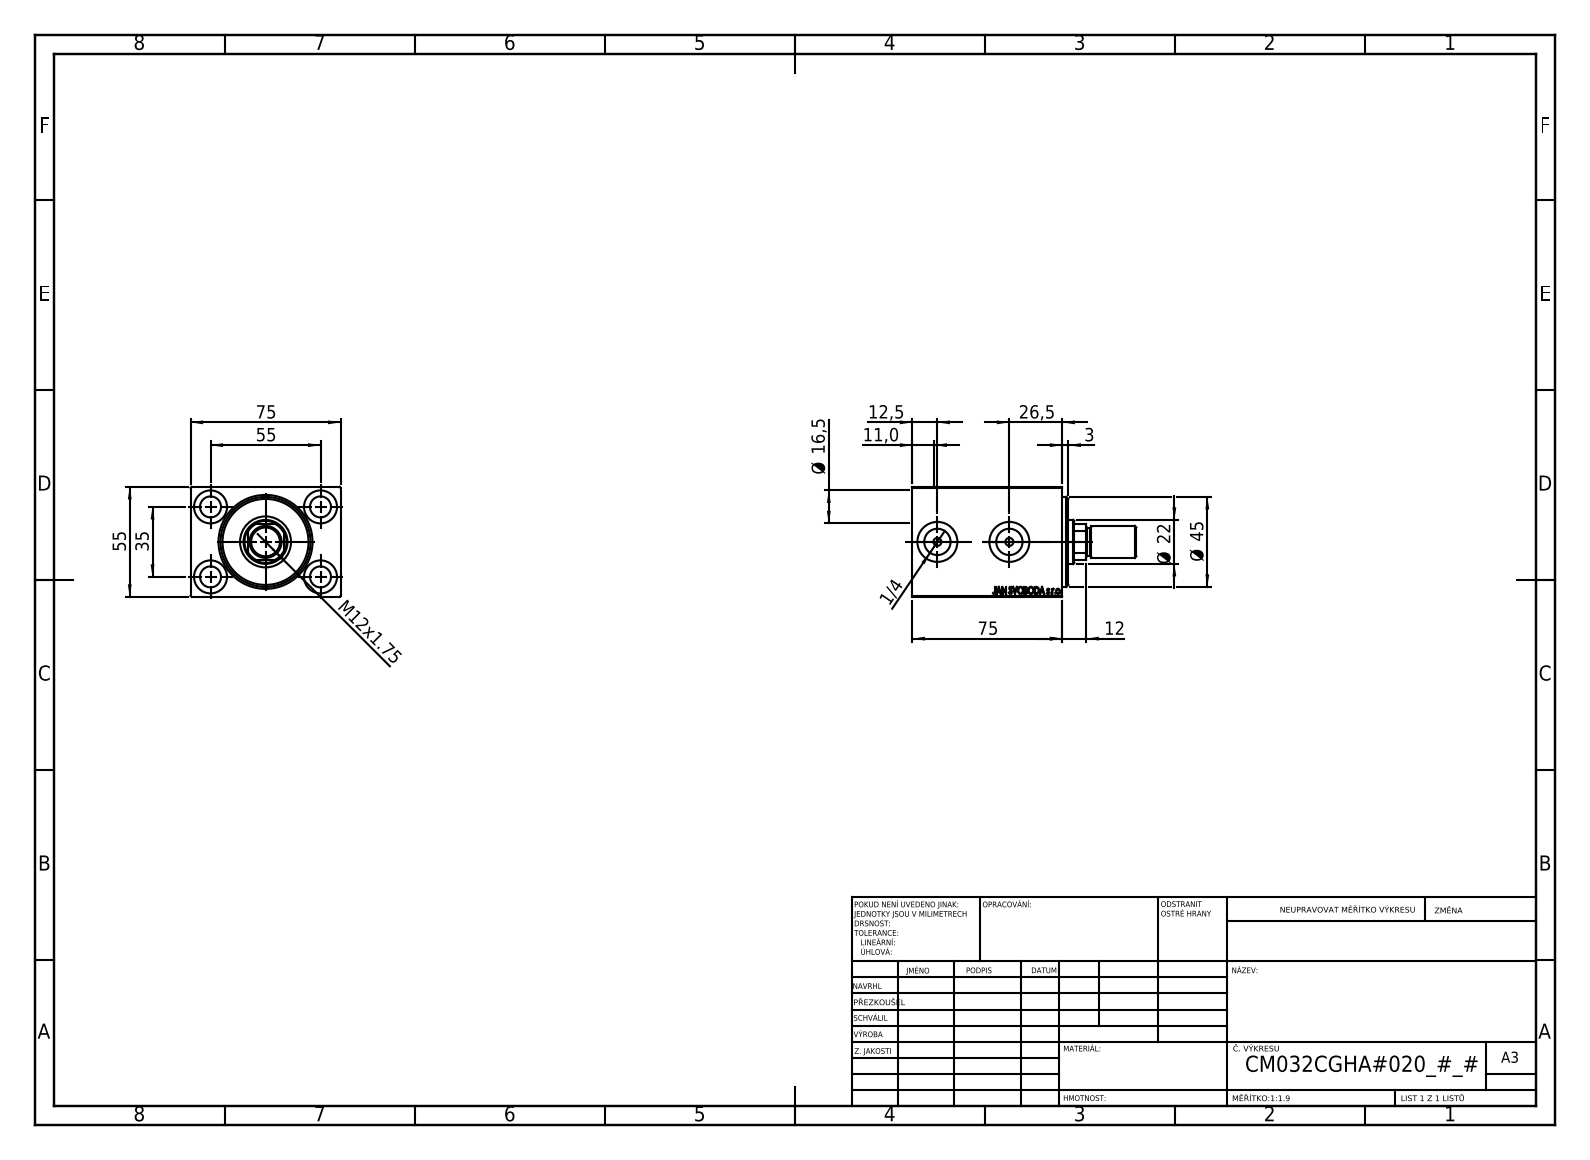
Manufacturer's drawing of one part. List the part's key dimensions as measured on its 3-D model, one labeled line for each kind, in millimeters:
Part name (STEP PRODUCT): V450CM_C_Body; V450CM_VC_B; V450CM_MALE_METRIC; V450CM_C_VCP
STEP written by: SolidWorks 2019 (CONFIG_CONTROL_DESIGN)
Units: millimetres
Bodies: 4 solids, 875 faces (411 planar, 64 cylindrical, 400 other)
Overall size (bounding box): 112 × 75 × 55
Volume: 270 589 mm³ · Surface area: 62 010 mm²
Round holes (diameter × count): ⌀10.5 ×5, ⌀16.5 ×4, ⌀4 ×2, ⌀13.16 ×2, ⌀20 ×2, ⌀22 ×1, ⌀25.5 ×1, ⌀32 ×1, ⌀34 ×1, ⌀45 ×1
Round bosses / shafts (diameter × count): ⌀16 ×1, ⌀14 ×1
Partial cylindrical surfaces — rounded edges, fillets, slot ends (radius × count): R10.5 ×1
Main face-to-face distances: 55, 75, 10, 65, 70, 5, 60, 53, 11, 64
Hole centre spacings: 32.6, 35, 55, 65.19, 36
